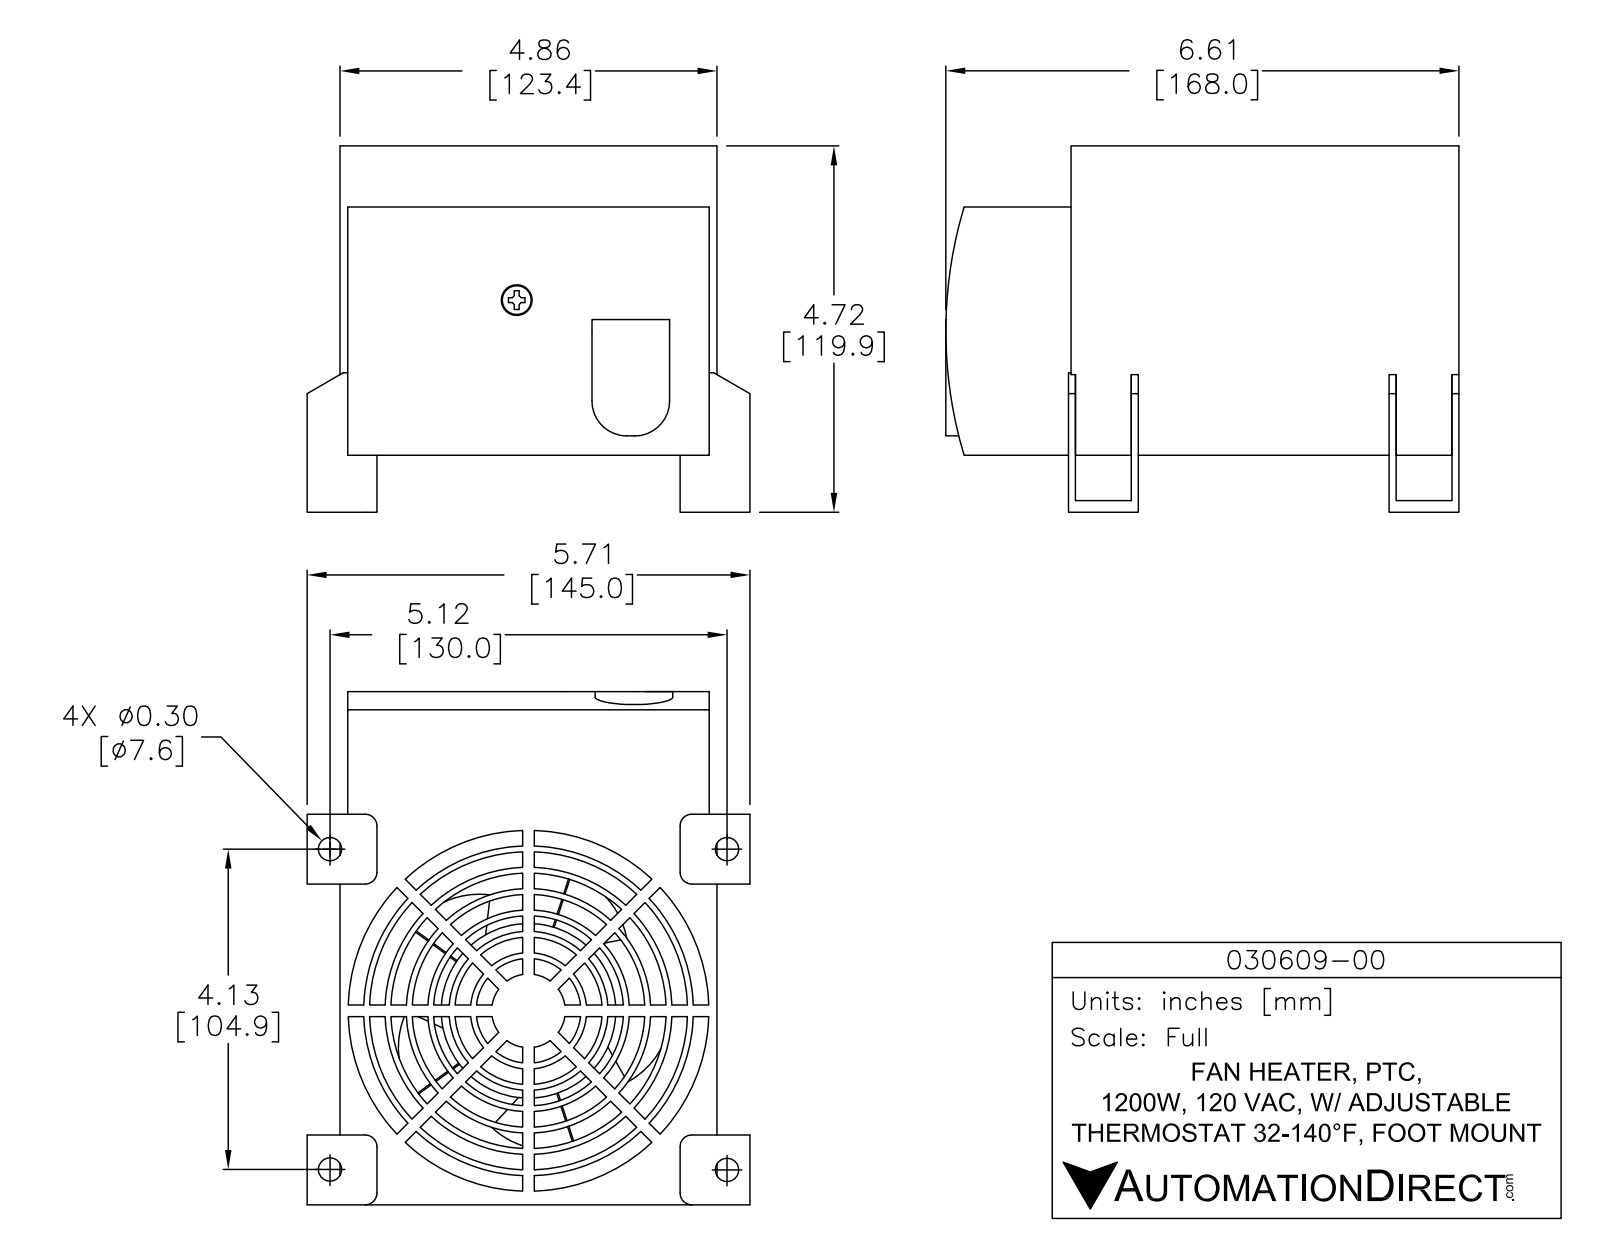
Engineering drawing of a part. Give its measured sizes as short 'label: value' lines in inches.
name: 030609-00
written by: SolidWorks 2013 (AUTOMOTIVE_DESIGN)
unit: in
bodies: 1 solid, 568 faces (310 planar, 233 cylindrical, 25 other)
size: 6.59 × 5.66 × 4.63
volume: 109.2 in³; area: 227.1 in²
holes: 4× ⌀0.21, 1× ⌀0.31, 1× ⌀0.36
bosses: 1× ⌀0.375, 1× ⌀0.238
rounds: 84× R0.07, 42× R0.04, 4× R0.03, 4× R0.06, 4× R0.175, 4× R0.395, 1× R0.4, 1× R2.66
face distances: 4.95, 0.25, 3.405, 3.655, 0.06, 3.465, 3.715, 0.22, 0.118, 4.833
hole spacings: 4.164, 5.161, 6.631
